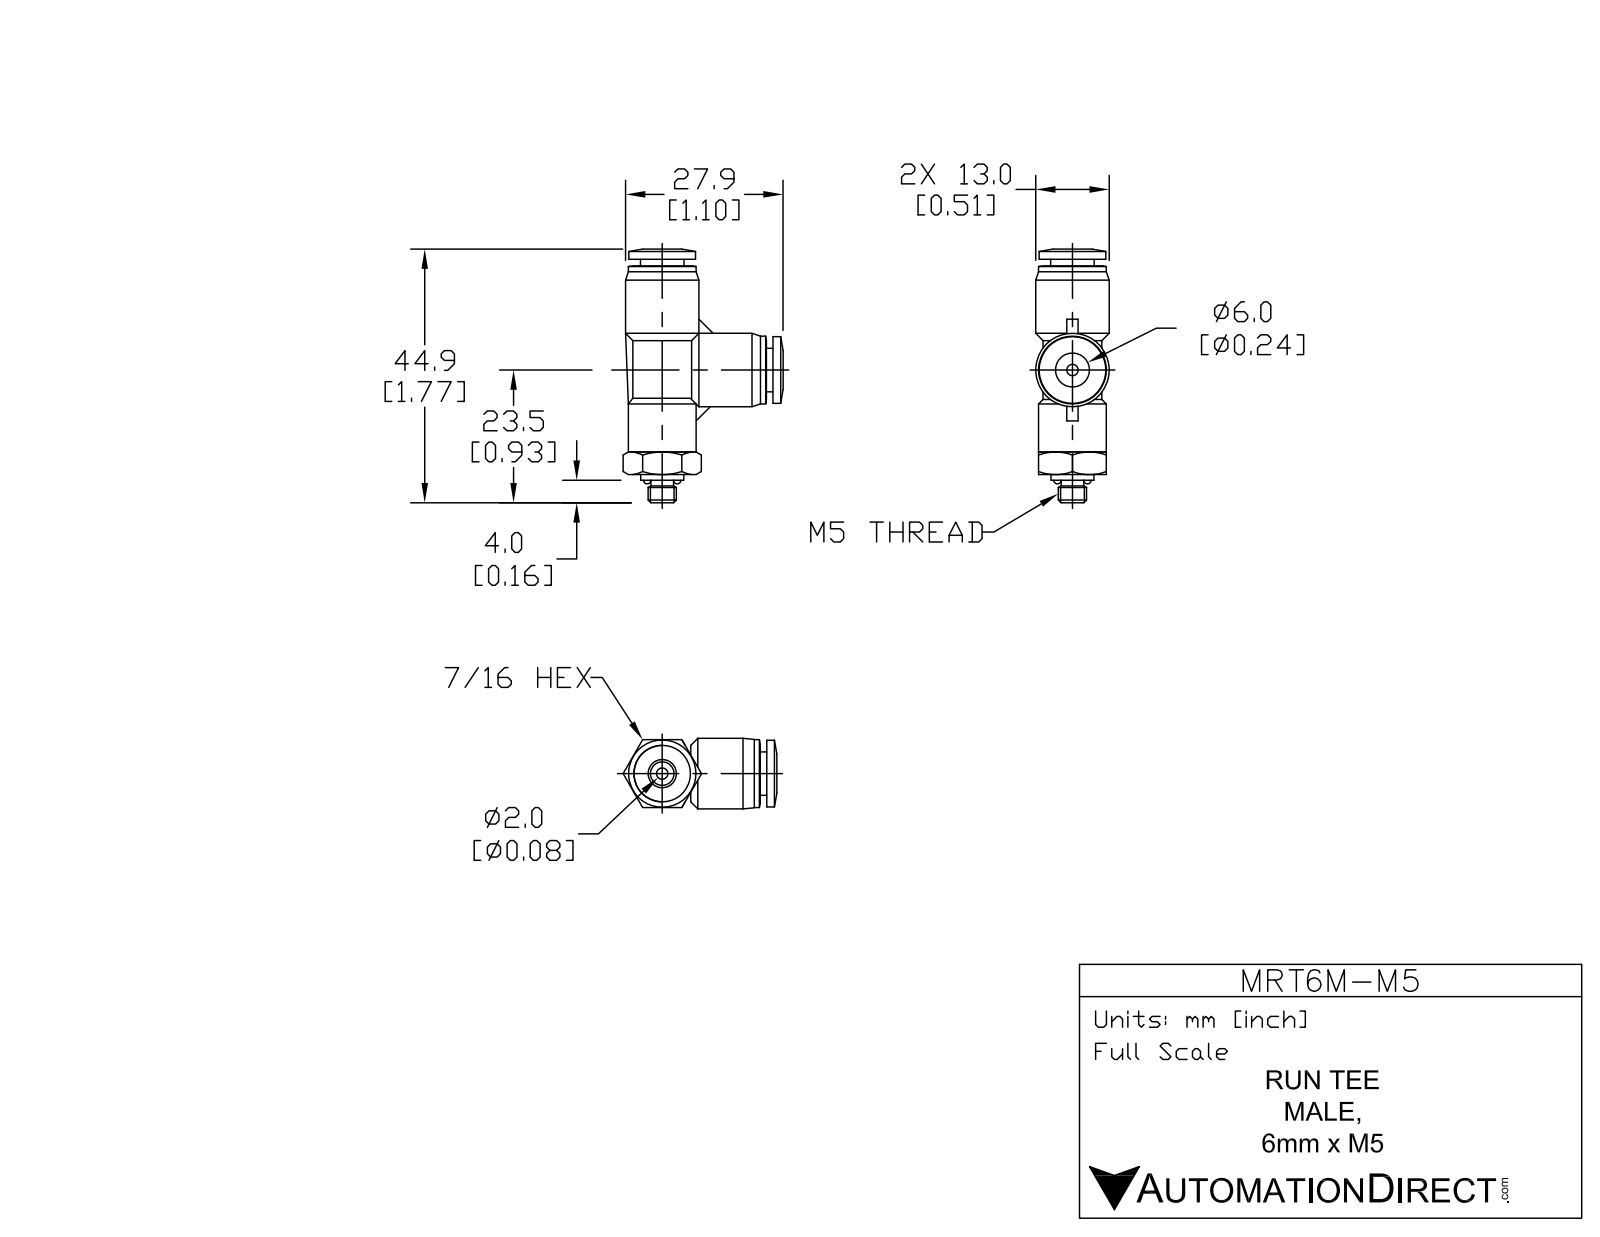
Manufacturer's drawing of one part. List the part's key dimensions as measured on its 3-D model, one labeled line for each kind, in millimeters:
Part name (STEP PRODUCT): MRT6M-M5
STEP written by: SolidWorks 2015 (AUTOMOTIVE_DESIGN)
Units: millimetres
Bodies: 2 solids, 118 faces (27 planar, 40 cylindrical, 51 other)
Overall size (bounding box): 44.4 × 28.3 × 13
Volume: 5 260 mm³ · Surface area: 3 731 mm²
Round holes (diameter × count): ⌀2.5 ×2, ⌀6.3 ×2
Round bosses / shafts (diameter × count): ⌀13 ×2, ⌀12 ×2, ⌀11.8 ×2, ⌀10.4 ×2, ⌀7.7 ×2, ⌀7.6 ×1, ⌀5 ×1, ⌀4 ×1
Main face-to-face distances: 1.1, 12, 37.6, 13.5, 14.6, 5, 7, 36.4, 23, 2
